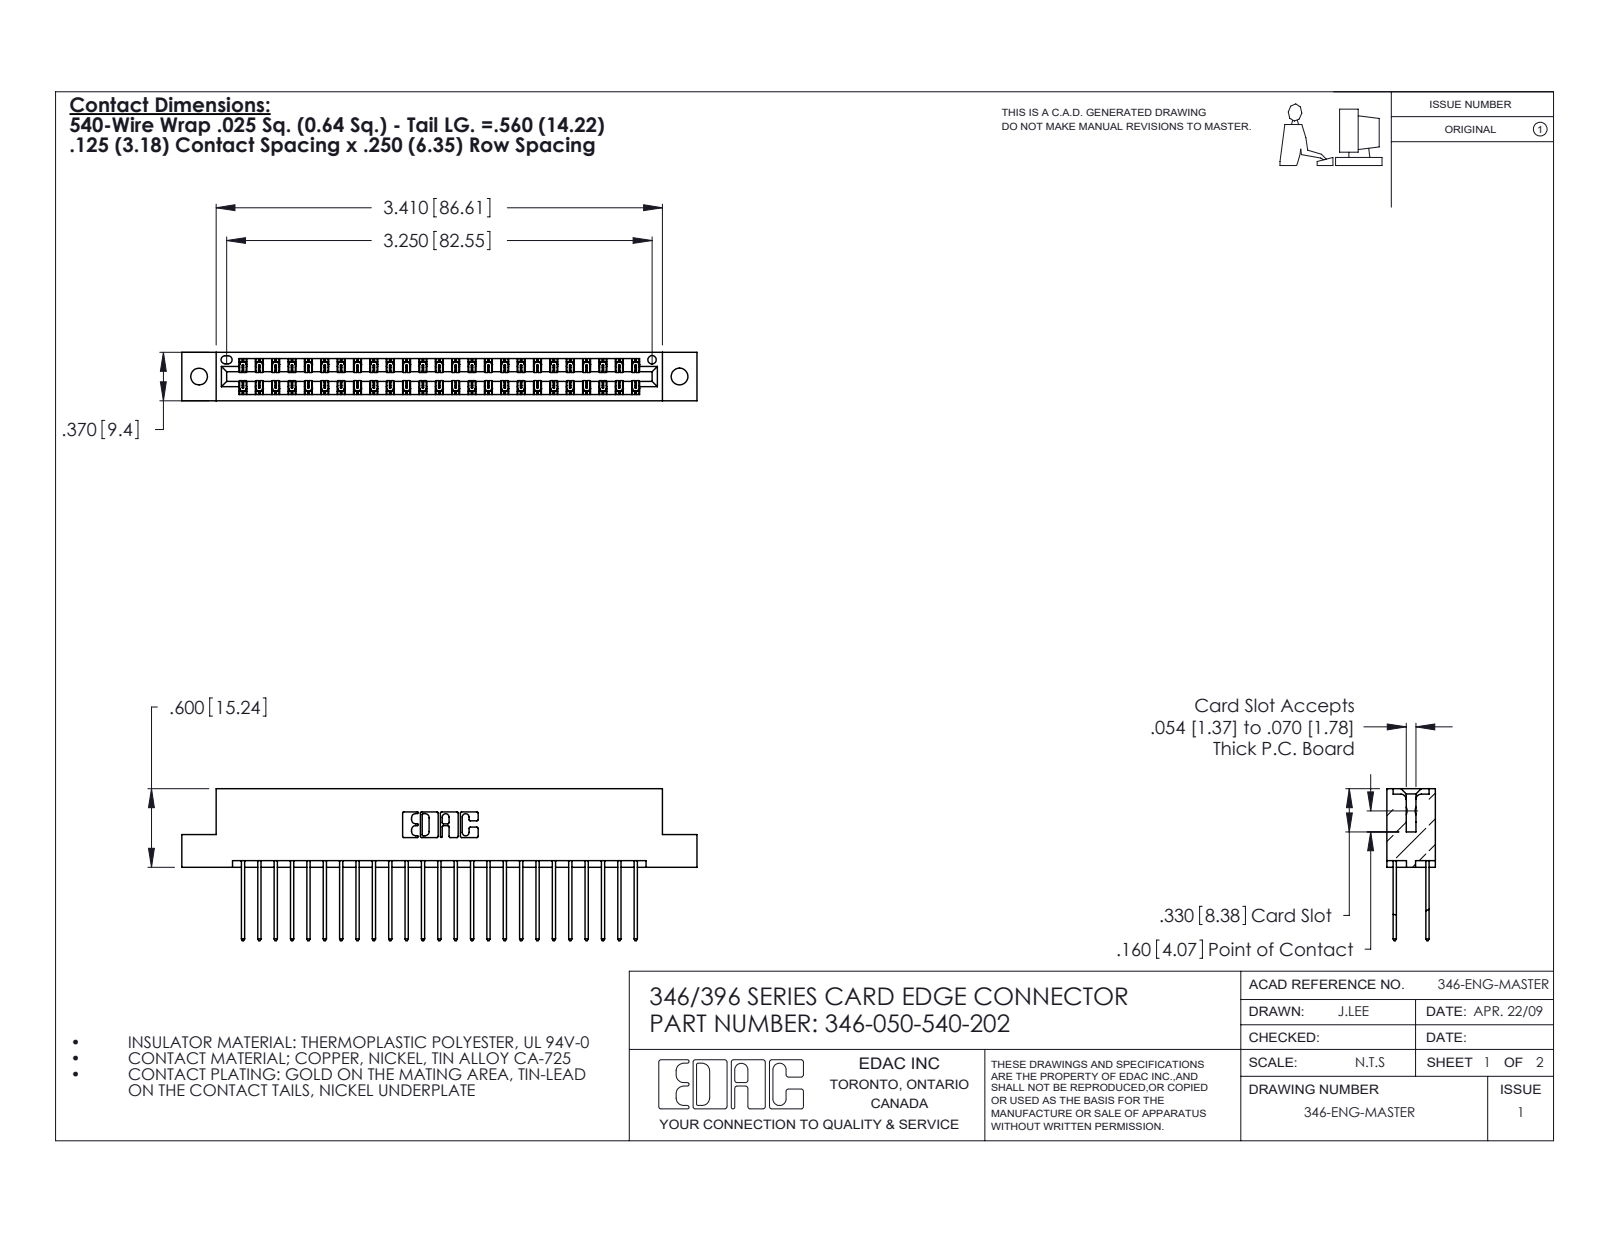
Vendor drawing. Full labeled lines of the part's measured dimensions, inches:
Part name (STEP PRODUCT): 346 Part_Flush Mounting Lugs - 0.128 Dia; 345-292-001_345-293-140; 346-050-540-202
STEP written by: SolidWorks 2020 (CONFIG_CONTROL_DESIGN)
Units: inches
Bodies: 51 solids, 2722 faces (1826 planar, 896 cylindrical, 0 other)
Overall size (bounding box): 3.935 × 1.16 × 0.37
Volume: 0.596 in³ · Surface area: 21.37 in²
Round holes (diameter × count): ⌀0.128 ×2, ⌀0.064 ×1
Partial cylindrical surfaces — rounded edges, fillets, slot ends (radius × count): R0.006 ×75, R0.01 ×50, R0.01 ×22, R0.007 ×6, R0.031 ×6, R0.026 ×3, R0.014 ×2, R0.022 ×2
Main face-to-face distances: 0.048, 0.322, 0.25, 0.072, 0.298, 0.025, 0.37, 0.275, 0.148, 0.222
Hole centre spacings: 0.246, 3.462, 3.67
